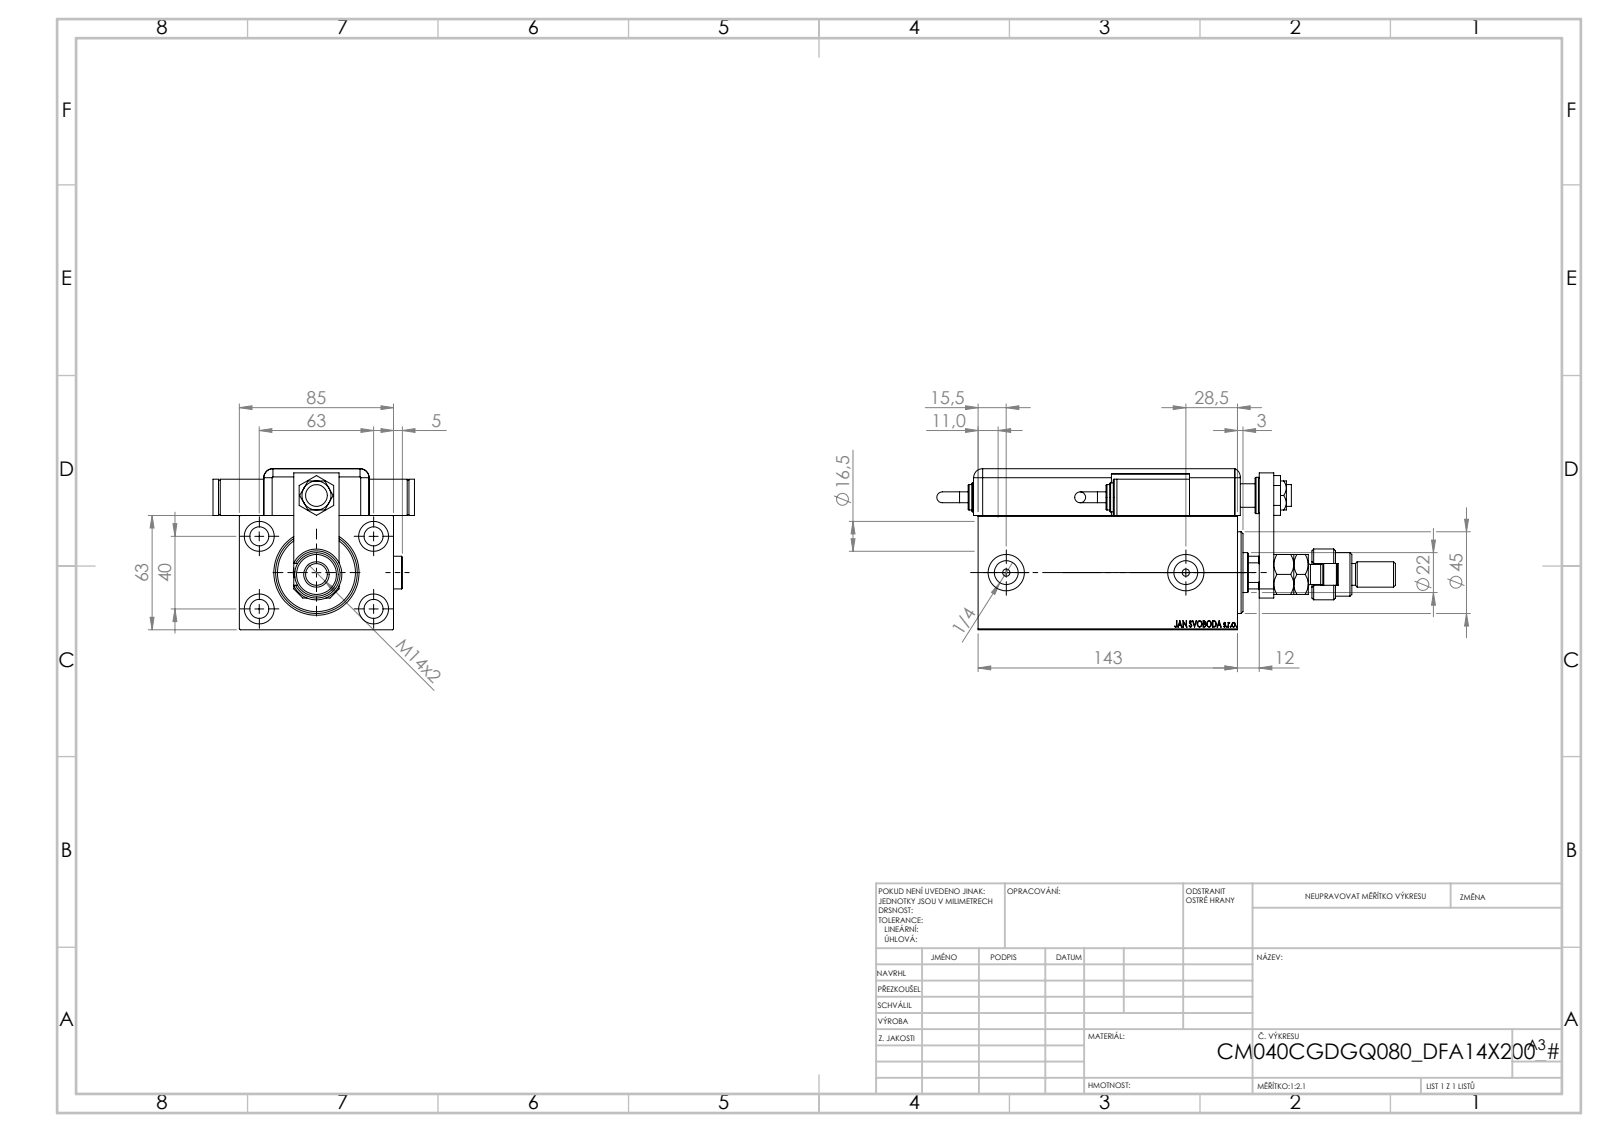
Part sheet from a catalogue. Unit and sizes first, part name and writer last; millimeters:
Units: millimetres
Overall size (bounding box): 252.76 × 111 × 88.8
Round holes (diameter × count): ⌀4 ×4, ⌀10.5 ×4, ⌀16.5 ×4, ⌀8 ×2, ⌀13.16 ×2, ⌀14 ×2, ⌀20 ×2, ⌀12 ×1, ⌀12.5 ×1, ⌀13 ×1, ⌀22 ×1, ⌀25.5 ×1
Round bosses / shafts (diameter × count): ⌀20 ×3, ⌀18 ×3, ⌀16 ×2, ⌀14 ×2, ⌀6 ×2, ⌀28 ×1, ⌀24 ×1, ⌀12 ×1
Partial cylindrical surfaces — rounded edges, fillets, slot ends (radius × count): R5 ×9, R9.75 ×1, R10 ×1, R10.5 ×1
Main face-to-face distances: 3, 63, 85, 13.5, 88.8, 25.8, 12, 16.5, 85.8, 22.8
Hole centre spacings: 37.31, 36.79, 37.86, 38.71, 40, 63, 69.99, 74.63
Volume: 815 534 mm³ · Surface area: 186 547 mm²
Bodies: 17 solids, 1385 faces (676 planar, 144 cylindrical, 565 other)
Part name (STEP PRODUCT): NUT_D19; MAGNETIC SWITCH Q; Q_T_W_DFA; Zatka_OIL_PORT (+7 more)
STEP written by: SolidWorks 2019 (CONFIG_CONTROL_DESIGN)
